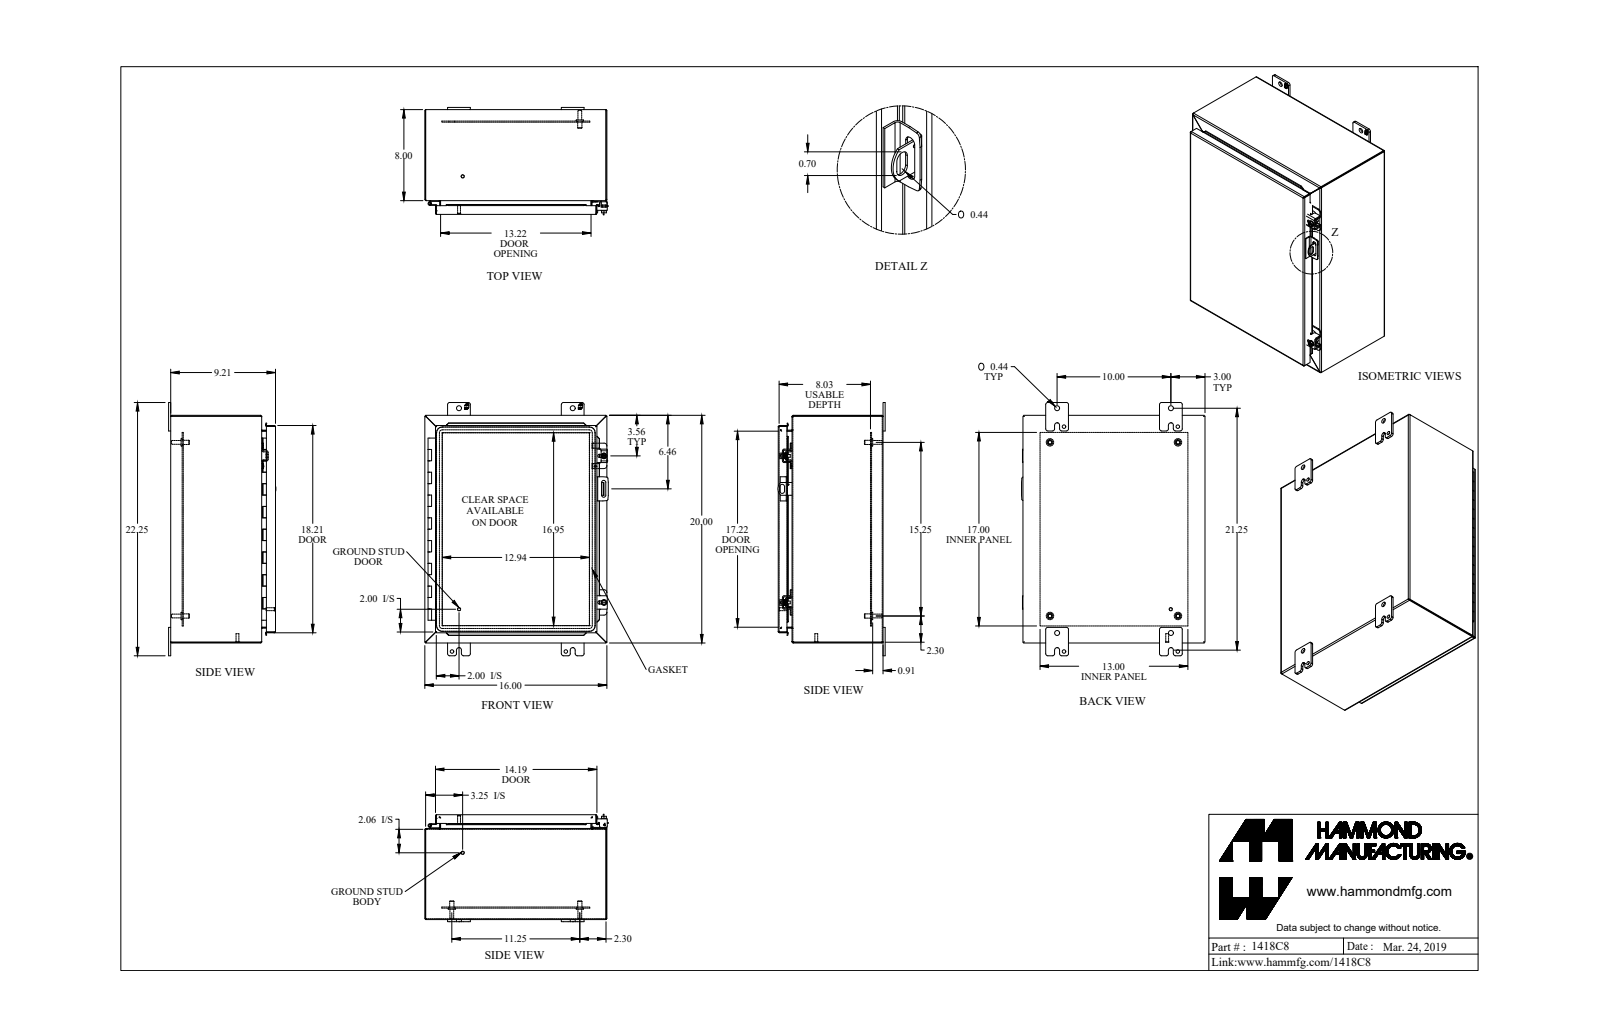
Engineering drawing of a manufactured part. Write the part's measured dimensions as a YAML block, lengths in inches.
part_name: "1418C8"
step_written_by: "SolidWorks 2019 (AUTOMOTIVE_DESIGN)"
units: inches
bodies: {solids: 37, faces: 909, planar: 642, cylindrical: 227, other: 40}
overall_size: [22.25, 16.125, 9.437]
volume: 308.9
surface_area: 3395
round_holes:
  - {diameter: 0.313, count: 4}
  - {diameter: 0.437, count: 4}
  - {diameter: 0.5, count: 4}
  - {diameter: 0.213, count: 2}
  - {diameter: 0.265, count: 2}
  - {diameter: 0.307, count: 2}
  - {diameter: 0.375, count: 2}
  - {diameter: 0.445, count: 2}
  - {diameter: 0.125, count: 1}
  - {diameter: 0.187, count: 1}
round_bosses_or_shafts:
  - {diameter: 0.65, count: 4}
  - {diameter: 0.375, count: 4}
  - {diameter: 0.33, count: 4}
  - {diameter: 1, count: 2}
  - {diameter: 0.5, count: 2}
  - {diameter: 0.39, count: 2}
  - {diameter: 0.281, count: 2}
  - {diameter: 0.25, count: 2}
partial_cylinders:
  - {radius: 0.188, count: 26}
  - {radius: 0.036, count: 16}
  - {radius: 0.108, count: 16}
  - {radius: 0.048, count: 13}
  - {radius: 0.143, count: 13}
  - {radius: 0.079, count: 8}
  - {radius: 0.218, count: 8}
  - {radius: 0.25, count: 8}
face_to_face_distances: [0.072, 9.113, 15.928, 9.185, 0.767, 8.346, 8.418, 19.928, 0.937, 1.009]
hole_center_spacings: [1.735, 10, 19.75, 22.137, 2.434, 14.223, 15.25, 18.261]
